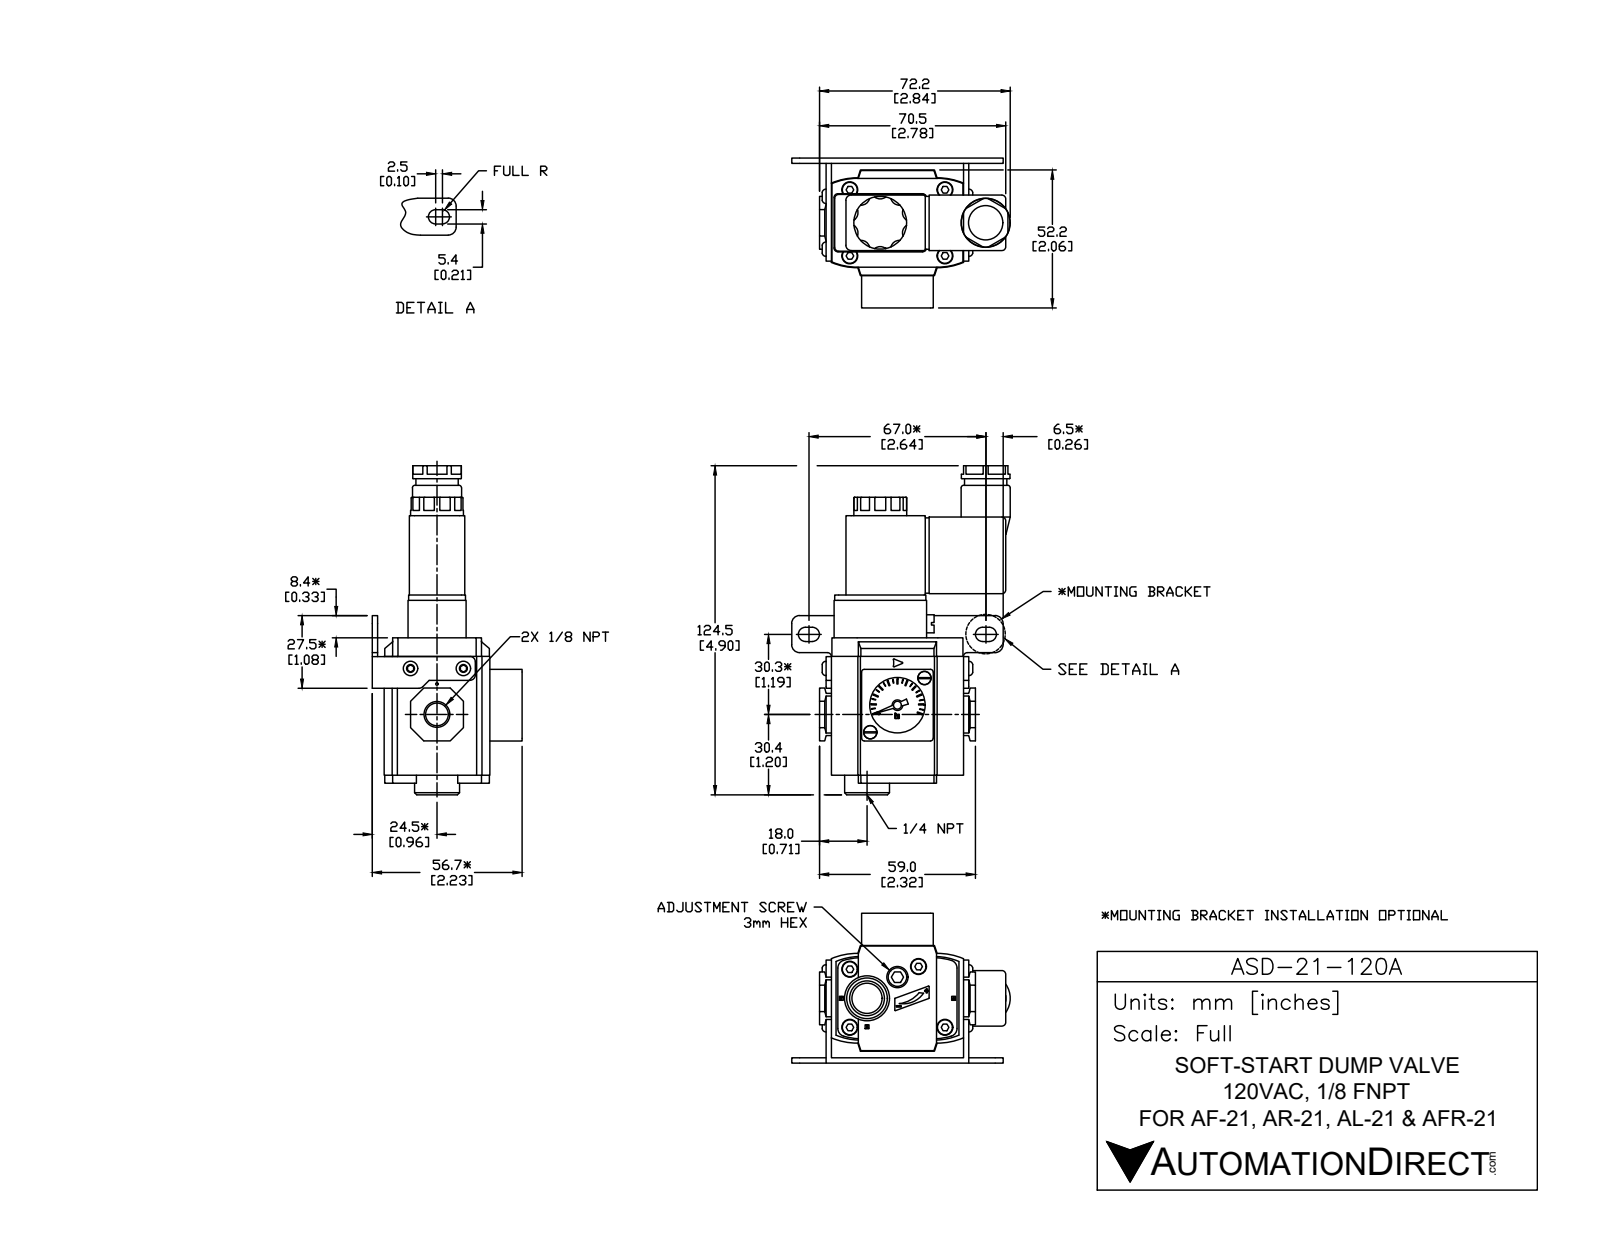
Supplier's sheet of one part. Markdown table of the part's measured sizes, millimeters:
| quantity | value |
| --- | --- |
| part name | ASD-21-120A |
| STEP written by | SolidWorks 2015 (CONFIG_CONTROL_DESIGN) |
| units | millimeters |
| bodies | 22 solids, 568 faces (363 planar, 168 cylindrical, 37 other) |
| overall size | 124.5 × 82.7 × 56.7 |
| volume | 166 361 mm³ |
| surface area | 46 436 mm² |
| round holes (diameter × count) | 3 × 10, 6 × 8, 7 × 1, 8 × 1, 8.43 × 1, 11.45 × 1, 13 × 1, 17 × 1, 21 × 1 |
| round bosses / shafts (diameter × count) | 5.6 × 4, 5.5 × 4, 2.5 × 2, 20 × 1, 18.6 × 1, 18.4 × 1, 16 × 1, 4 × 1 |
| partial cylindrical surfaces (radius × count) | 1.5 × 10, 3.16 × 10, 1 × 6, 3 × 6, 0.73 × 4, 1.25 × 4, 2.7 × 4, 24.8 × 4 |
| main face-to-face distances | 52, 3, 2, 27.5, 6.5, 7, 45, 14, 5.5, 2.5 |
| hole center spacings | 1.5, 23.5, 36, 36.03, 42.99, 12.78, 14.09, 14.5 |
